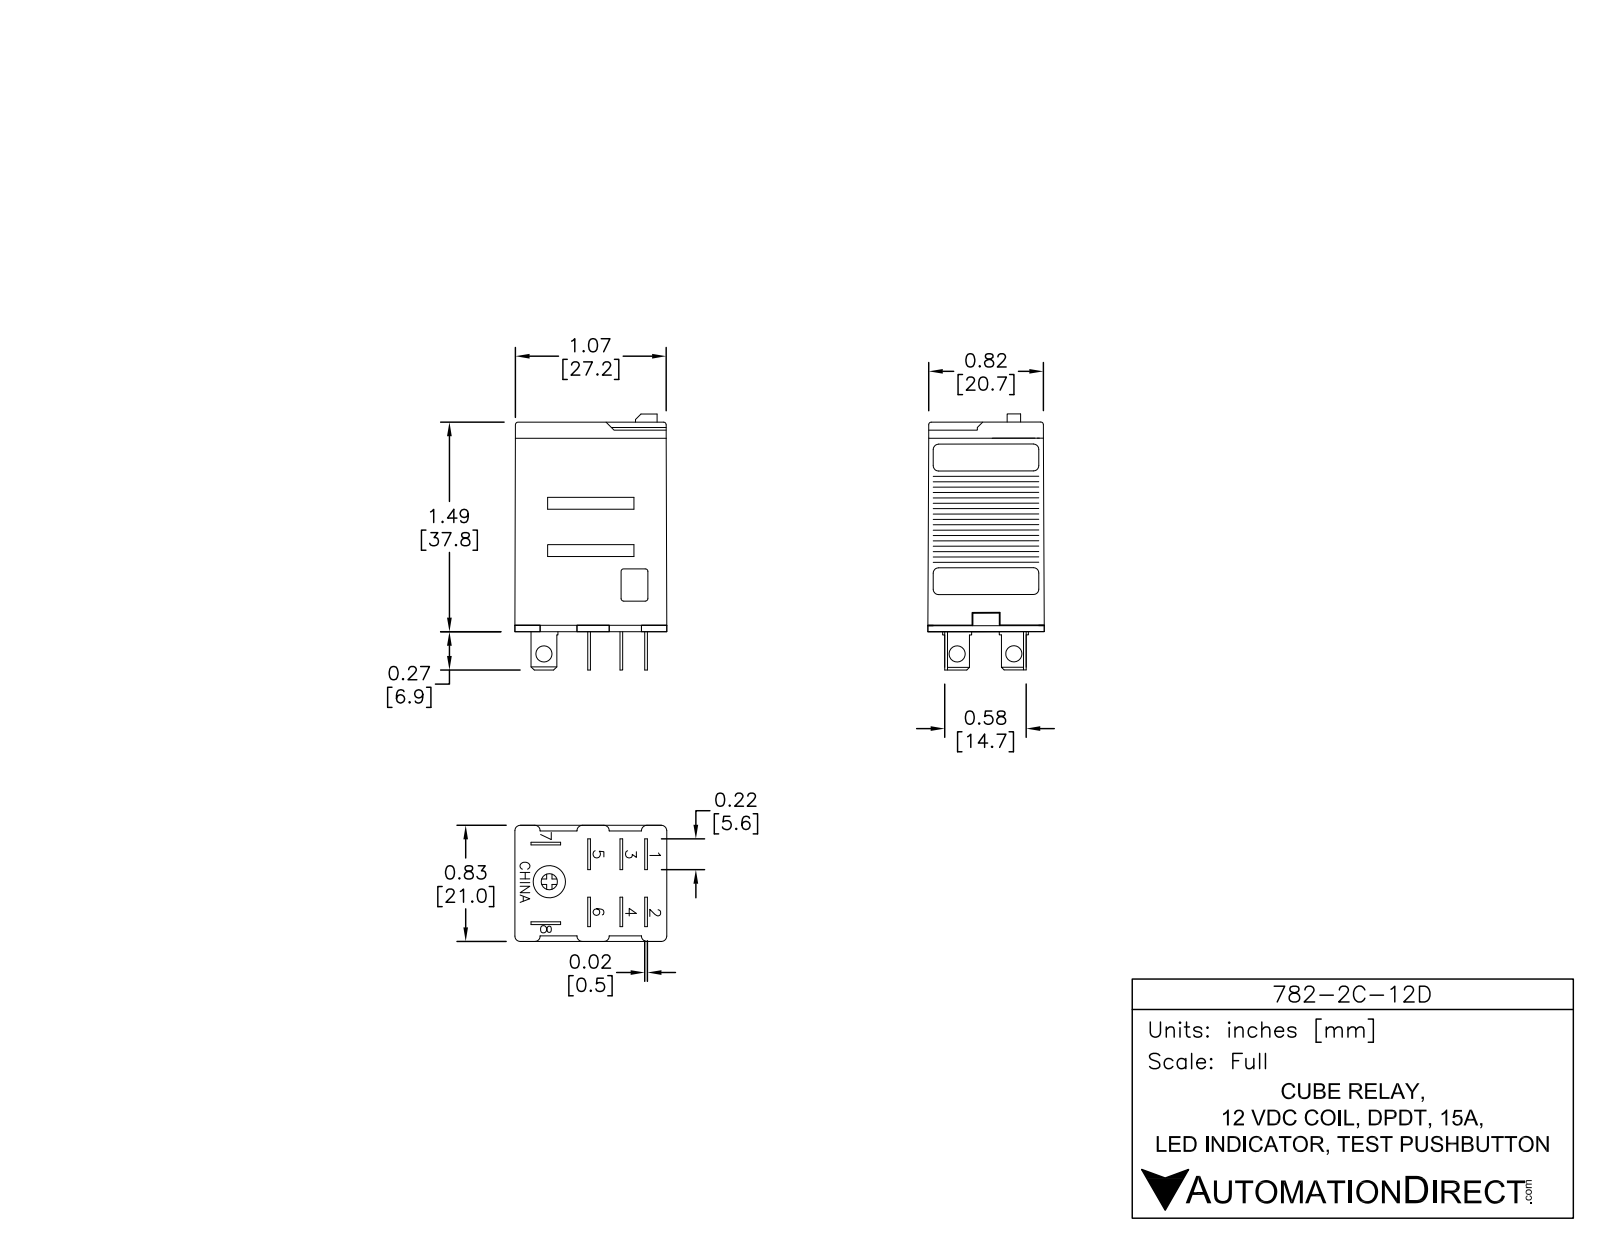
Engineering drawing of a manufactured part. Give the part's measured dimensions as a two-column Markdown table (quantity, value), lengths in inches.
| quantity | value |
| --- | --- |
| part name | 782-2C-12D |
| STEP written by | SolidWorks 2021 (CONFIG_CONTROL_DESIGN) |
| units | inches |
| bodies | 1 solid, 197 faces (176 planar, 21 cylindrical, 0 other) |
| overall size | 1.83 × 1.1 × 0.83 |
| volume | 1.401 in³ |
| surface area | 8.801 in² |
| round holes (diameter × count) | 0.11 × 3, 0.085 × 1 |
| round bosses / shafts (diameter × count) | 0.07 × 1 |
| partial cylindrical surfaces (radius × count) | 0.24 × 1 |
| main face-to-face distances | 0.83, 1.1, 1.54, 0.02, 0.232, 0.03, 0.04, 1.53, 1.5, 0.185 |
| hole center spacings | 0.45 |
